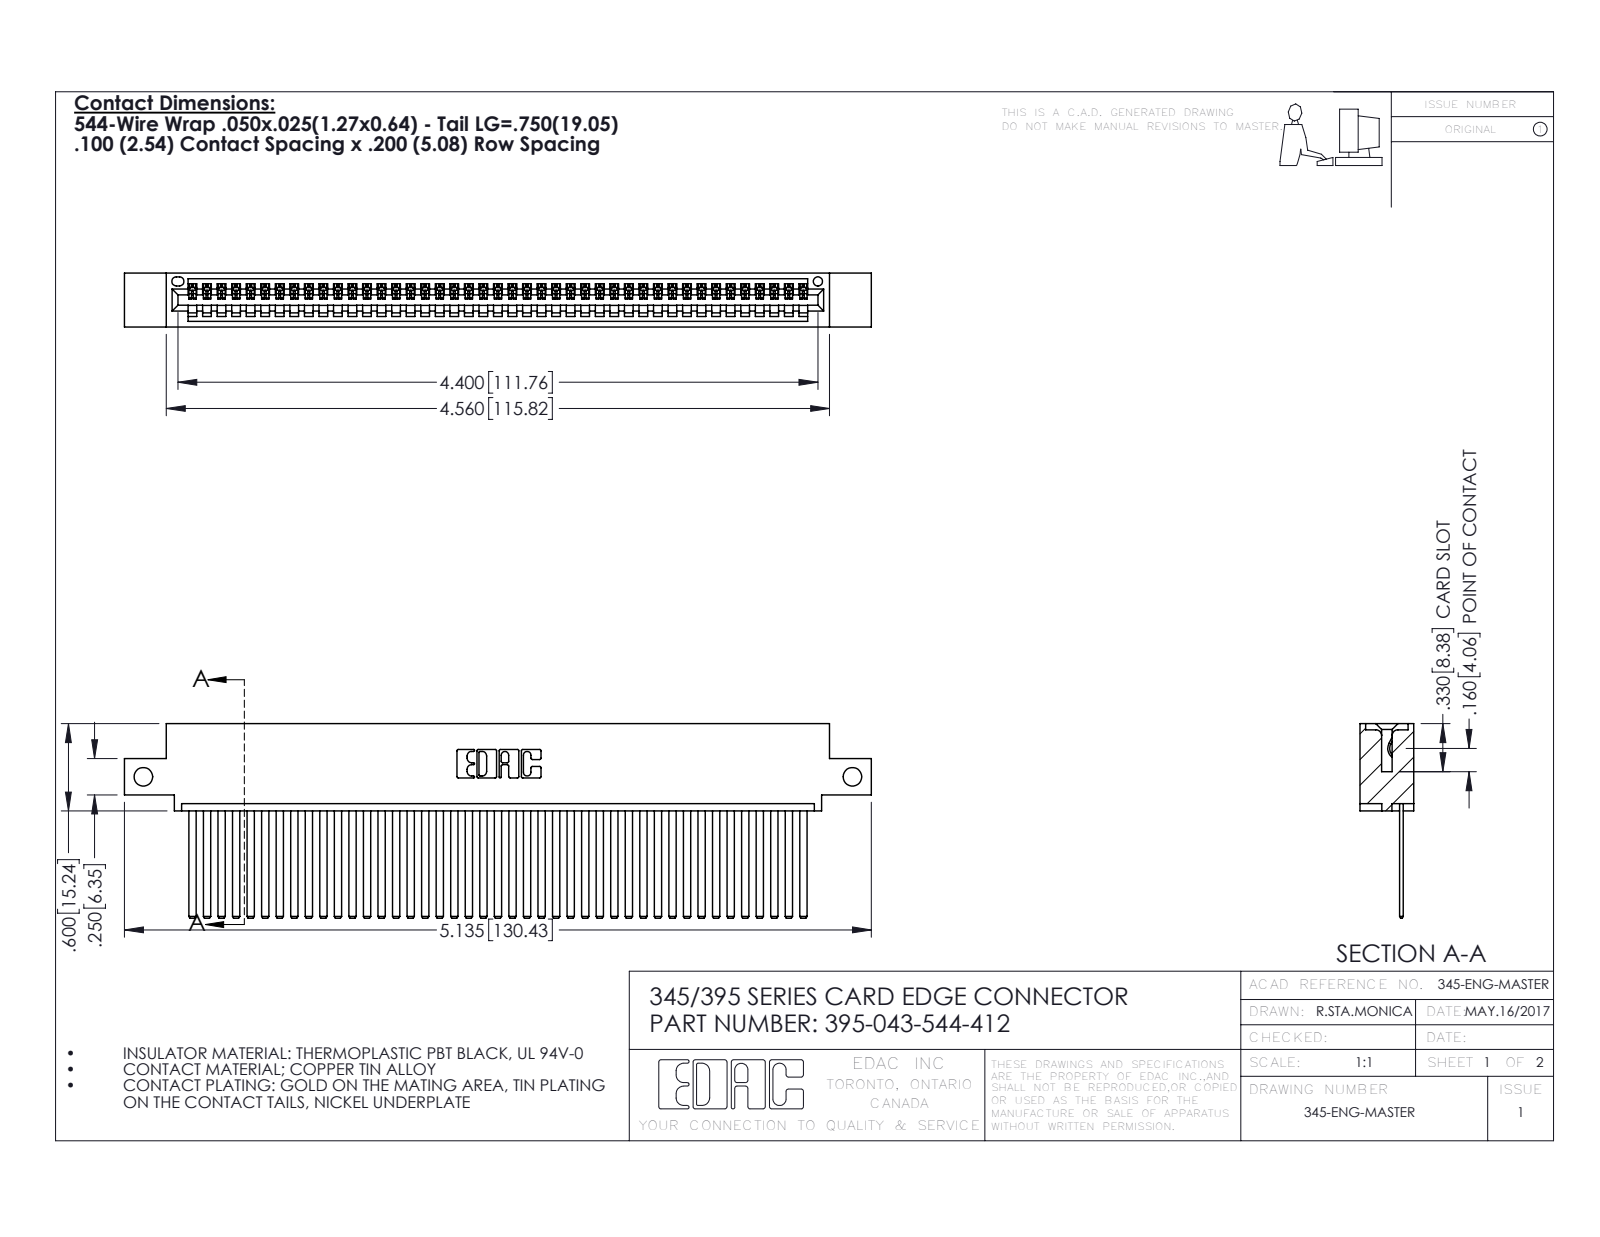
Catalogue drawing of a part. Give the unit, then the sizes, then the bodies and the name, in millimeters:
Units: millimetres
Overall size (bounding box): 130.4 × 34 × 9.4
Round holes (diameter × count): ⌀3.3 ×2, ⌀1.6 ×1
Partial cylindrical surfaces — rounded edges, fillets, slot ends (radius × count): R0.2 ×86, R0.3 ×22, R0.2 ×6, R0.8 ×6, R0.7 ×3, R0.8 ×2, R1 ×2, R0.4 ×1
Main face-to-face distances: 1.8, 7.6, 0.6, 2.5, 6.9, 9.4, 5.1, 5.7, 3.8, 1.8
Hole centre spacings: 123.8
Volume: 12 700 mm³ · Surface area: 18 370 mm²
Bodies: 44 solids, 2366 faces (1632 planar, 734 cylindrical, 0 other)
Part name (STEP PRODUCT): 395-043-544-412; 345 Part_0.110 Offset - Side Mount; 345-292-001_345-293-144
STEP written by: SolidWorks 2016 (CONFIG_CONTROL_DESIGN)
